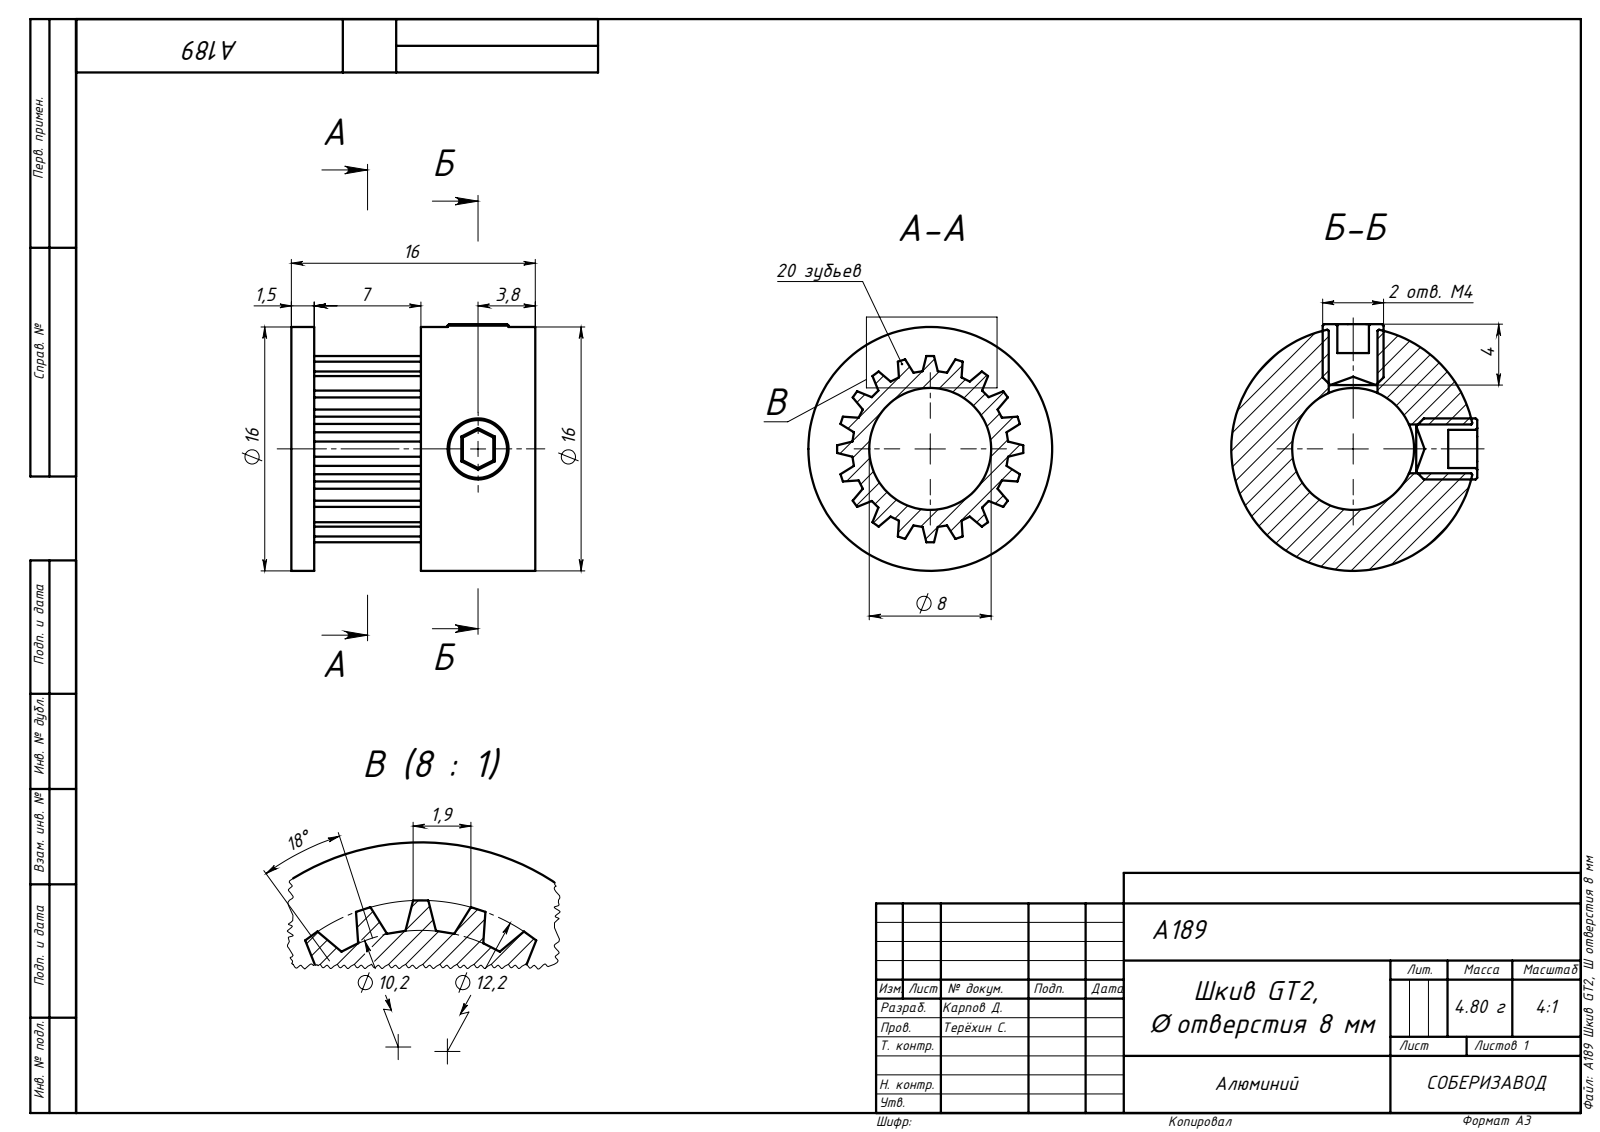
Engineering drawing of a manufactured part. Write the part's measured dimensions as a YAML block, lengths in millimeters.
part_name: "A189 Шкив GT2, O отверстия 8 мм(подробная модель); A189 Шкив GT2, O отверстия 8 мм"
step_written_by: "SolidWorks 2019 (AUTOMOTIVE_DESIGN)"
units: millimeters
bodies: {solids: 3, faces: 142, planar: 112, cylindrical: 14, other: 16}
overall_size: [16.19, 16.14, 16]
volume: 1701
surface_area: 2026
round_holes:
  - {diameter: 3.2, count: 2}
  - {diameter: 8, count: 1}
round_bosses_or_shafts:
  - {diameter: 4, count: 2}
  - {diameter: 16, count: 1}
face_to_face_distances: [16, 8.5, 7.5, 1.5, 7, 14.5, 3.45, 3.44, 10.24, 12.21]
